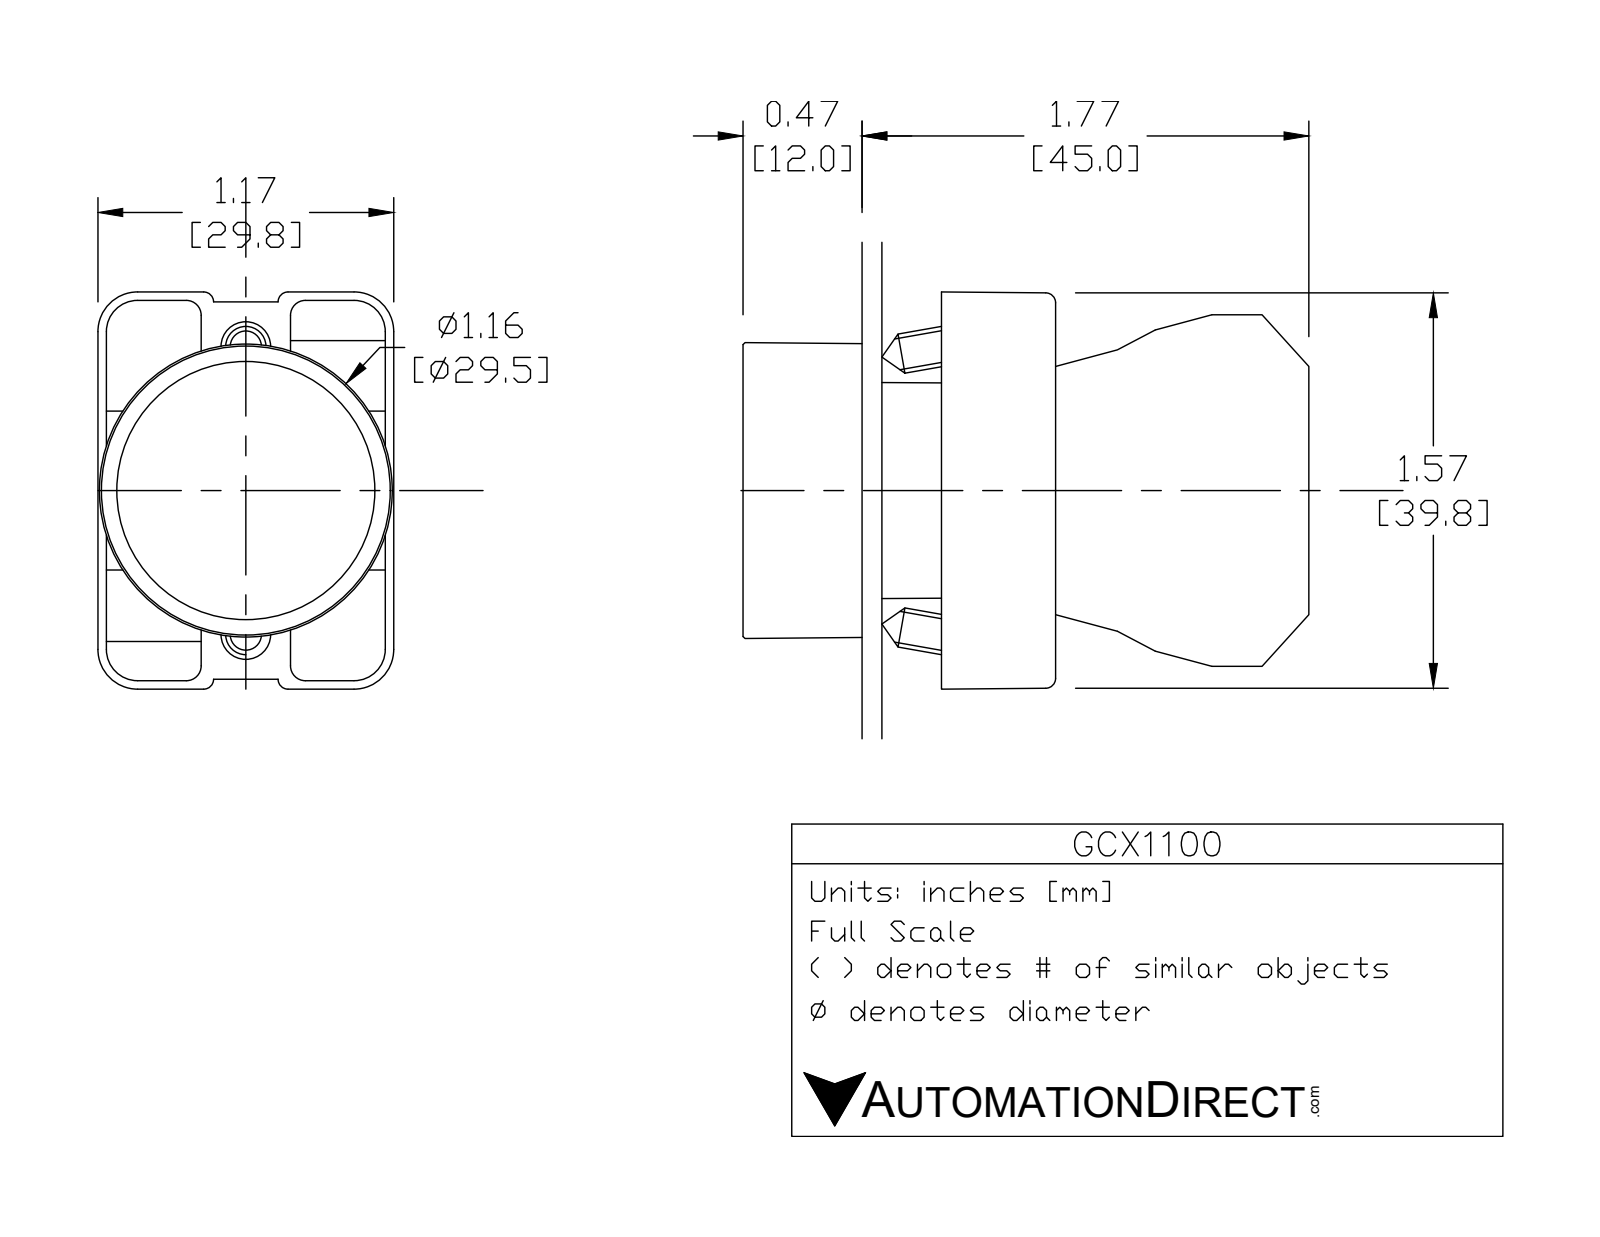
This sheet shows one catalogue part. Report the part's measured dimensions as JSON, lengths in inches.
{"part_name": "ecx1029; ecx1040; GCX1100 OPERATOR; GCX1100", "step_written_by": "SolidWorks 2016 (AUTOMOTIVE_DESIGN)", "units": "inches", "bodies": {"solids": 6, "faces": 381, "planar": 222, "cylindrical": 132, "other": 27}, "overall_size": [2.217, 1.581, 1.177], "volume_in3": 1.741, "surface_area_in2": 27.14, "round_holes": [[0.079, 2], [0.124, 2], [0.13, 2], [0.087, 1], [0.197, 1], [0.878, 1], [0.888, 1], [1.024, 1]], "round_bosses_or_shafts": [[0.157, 2], [1.175, 1], [1.004, 1], [0.945, 1], [0.856, 1], [0.78, 1]], "partial_cylinders_radius": [[0.059, 24], [0.041, 12], [0.124, 12], [0.157, 12], [0.039, 4], [0.128, 2], [0.02, 1], [0.063, 1]], "face_to_face_distances": [0.72, 0.579, 0.033, 0.472, 1.193, 0.031, 0.689, 0.598, 1.161, 1.071], "hole_center_spacings": [0.236, 0.544, 0.472, 0.49]}
